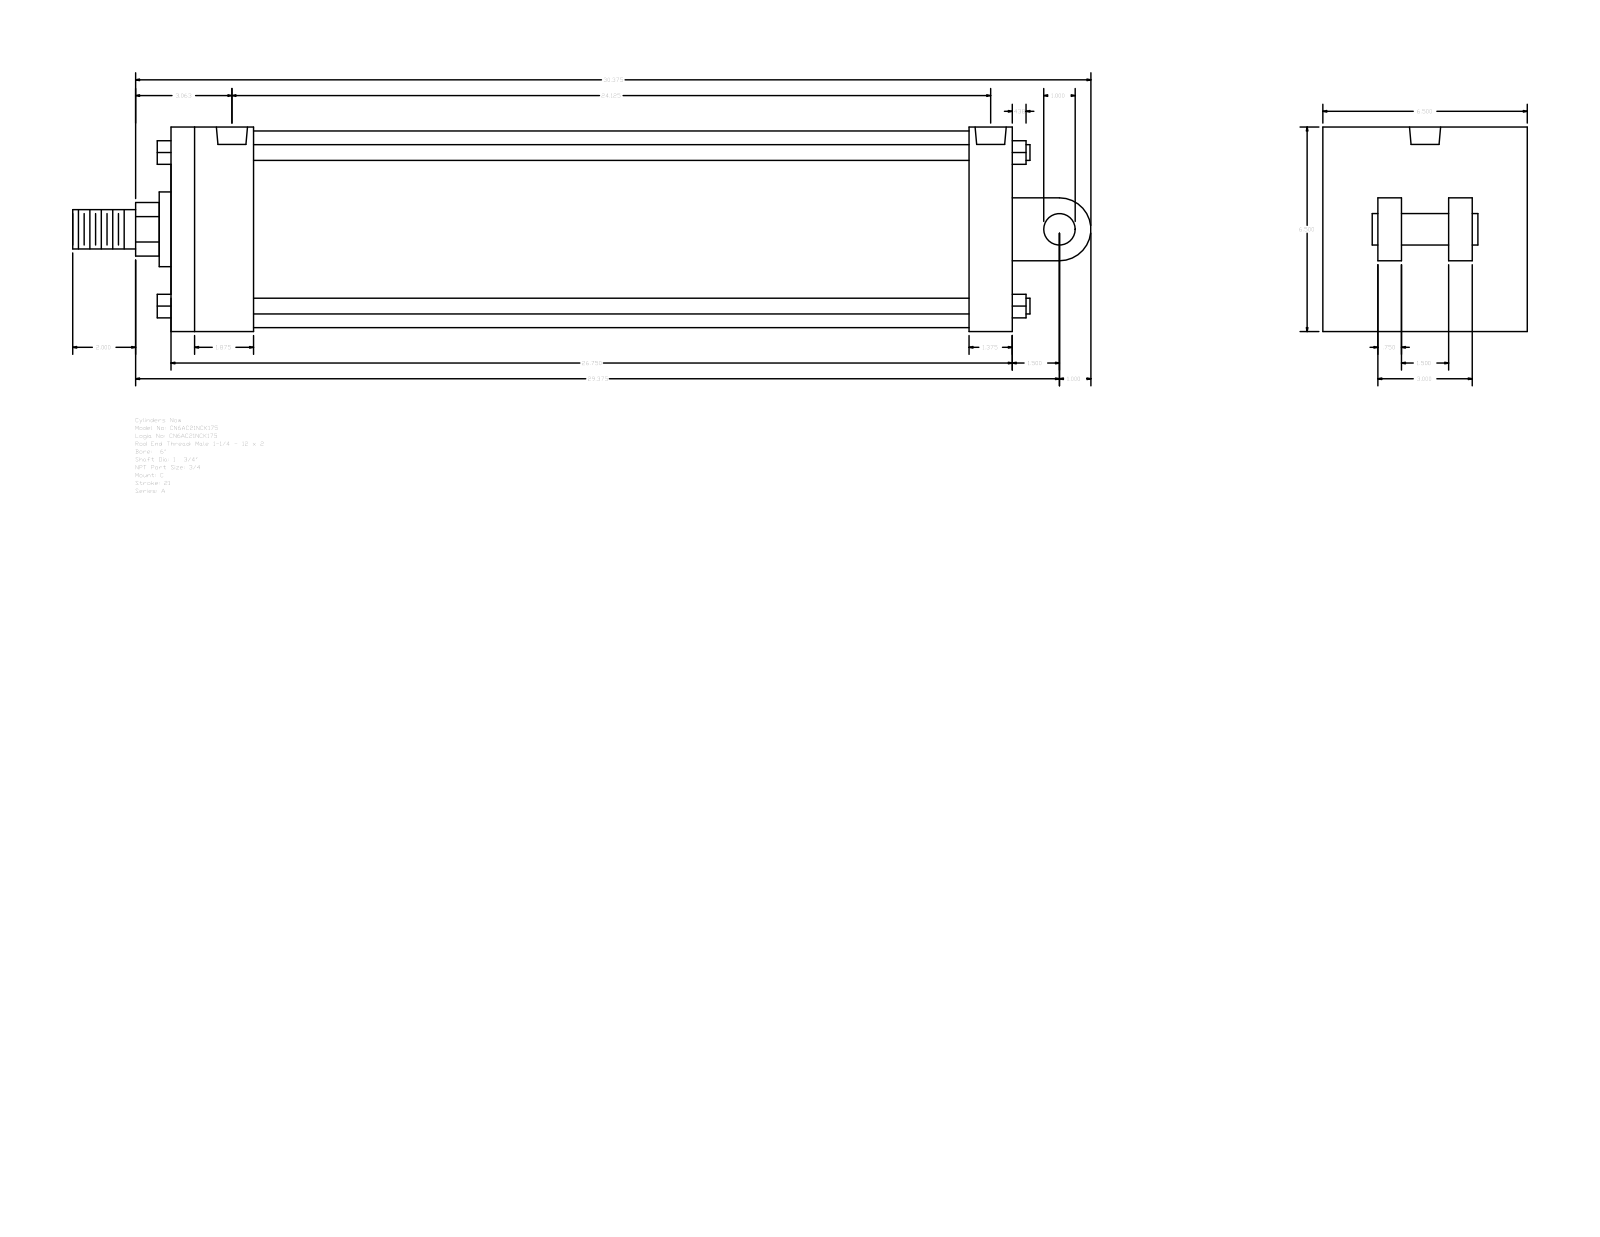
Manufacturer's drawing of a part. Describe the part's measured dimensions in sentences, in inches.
The part is named "A_C__0600_1.75". Its 3-D file was written by "GSSL Pune (CONFIG_CONTROL_DESIGN)". It is 0 solids with 135 faces: 102 planar, 33 cylindrical and 0 other. Overall it measures 32.375 by 6.5 by 6.5 inches. Round holes: 4 of diameter 0.594, 2 of diameter 0.989. Round bosses or shafts: 4 of diameter 0.5, 1 of diameter 6.25, 1 of diameter 2.375, 1 of diameter 1.75, 1 of diameter 1.25, 1 of diameter 1. Partial cylindrical surfaces (rounded edges, fillets, slot ends): 1 of radius 0.852, 1 of radius 1. The main face-to-face distances are 6.5, 26.75, 0.75, 2.25, 2.625, 24.125, 25.375, 22.75, 1.375, 2.5. The hole center spacings are 0.219, 23.687, 23.906, 24.125.
